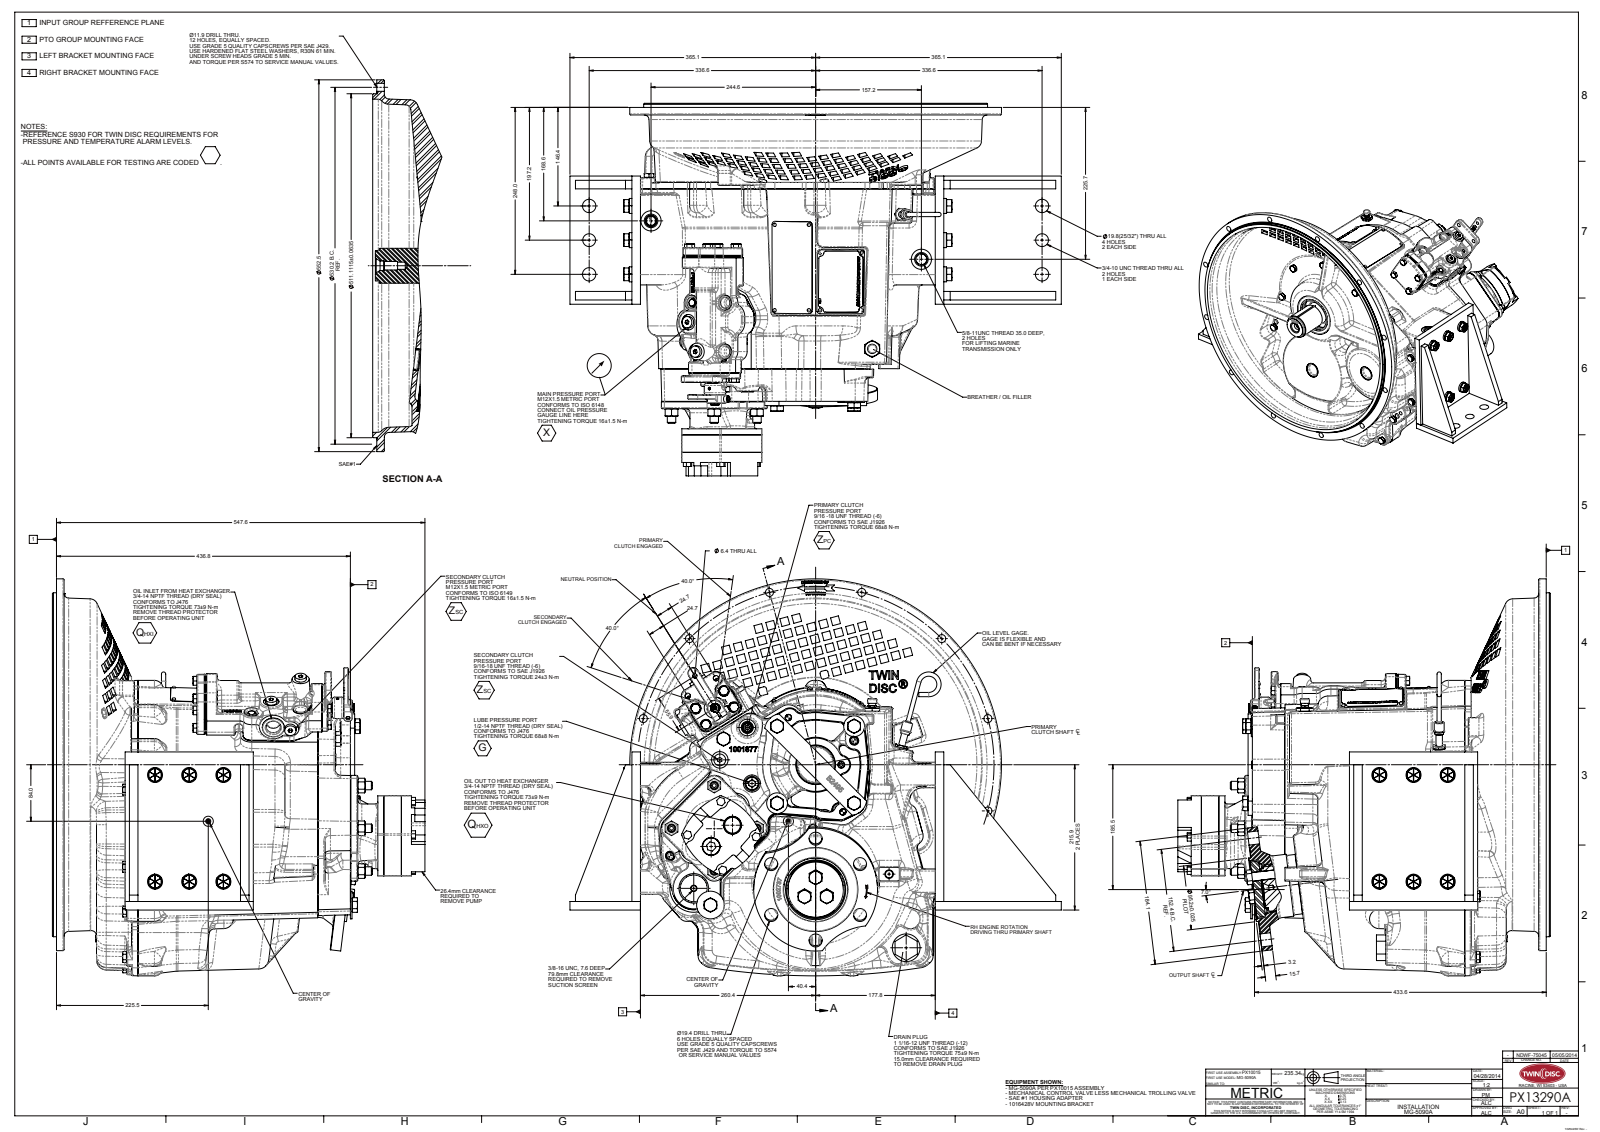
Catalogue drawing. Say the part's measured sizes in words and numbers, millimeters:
The part is named "PX13290A". Its 3-D file was written by "SolidWorks 2010 (AUTOMOTIVE_DESIGN)". It is 0 solids with 4159 faces: 1326 planar, 830 cylindrical and 2003 other. Overall it measures 730.25 by 589.91 by 553.65 millimeters. Round holes: 12 of diameter 11.91, 6 of diameter 19.45, 5 of diameter 8, 4 of diameter 19.84, 3 of diameter 11.13, 2 of diameter 7.94, 2 of diameter 9.51, 2 of diameter 16.67, 2 of diameter 19.05, 2 of diameter 24.61, 2 of diameter 29.97, 1 of diameter 2.55. Round bosses or shafts: 8 of diameter 18.87, 8 of diameter 14.14, 6 of diameter 22.33, 4 of diameter 12.54, 3 of diameter 22.35, 3 of diameter 17, 2 of diameter 30.99, 2 of diameter 17.46. Partial cylindrical surfaces (rounded edges, fillets, slot ends): 50 of radius 8.13, 45 of radius 1.52, 35 of radius 2.03, 33 of radius 3.05, 33 of radius 12.7, 25 of radius 1.5, 17 of radius 3, 16 of radius 6.4. The main face-to-face distances are 12.7, 450.85, 0.78, 165.1, 48.54, 438.15, 267.33, 268.11, 0.42, 266.91. The hole center spacings are 76.2, 459.18, 137.23, 265.1, 265.11, 374.92, 512.14, 131.98.
